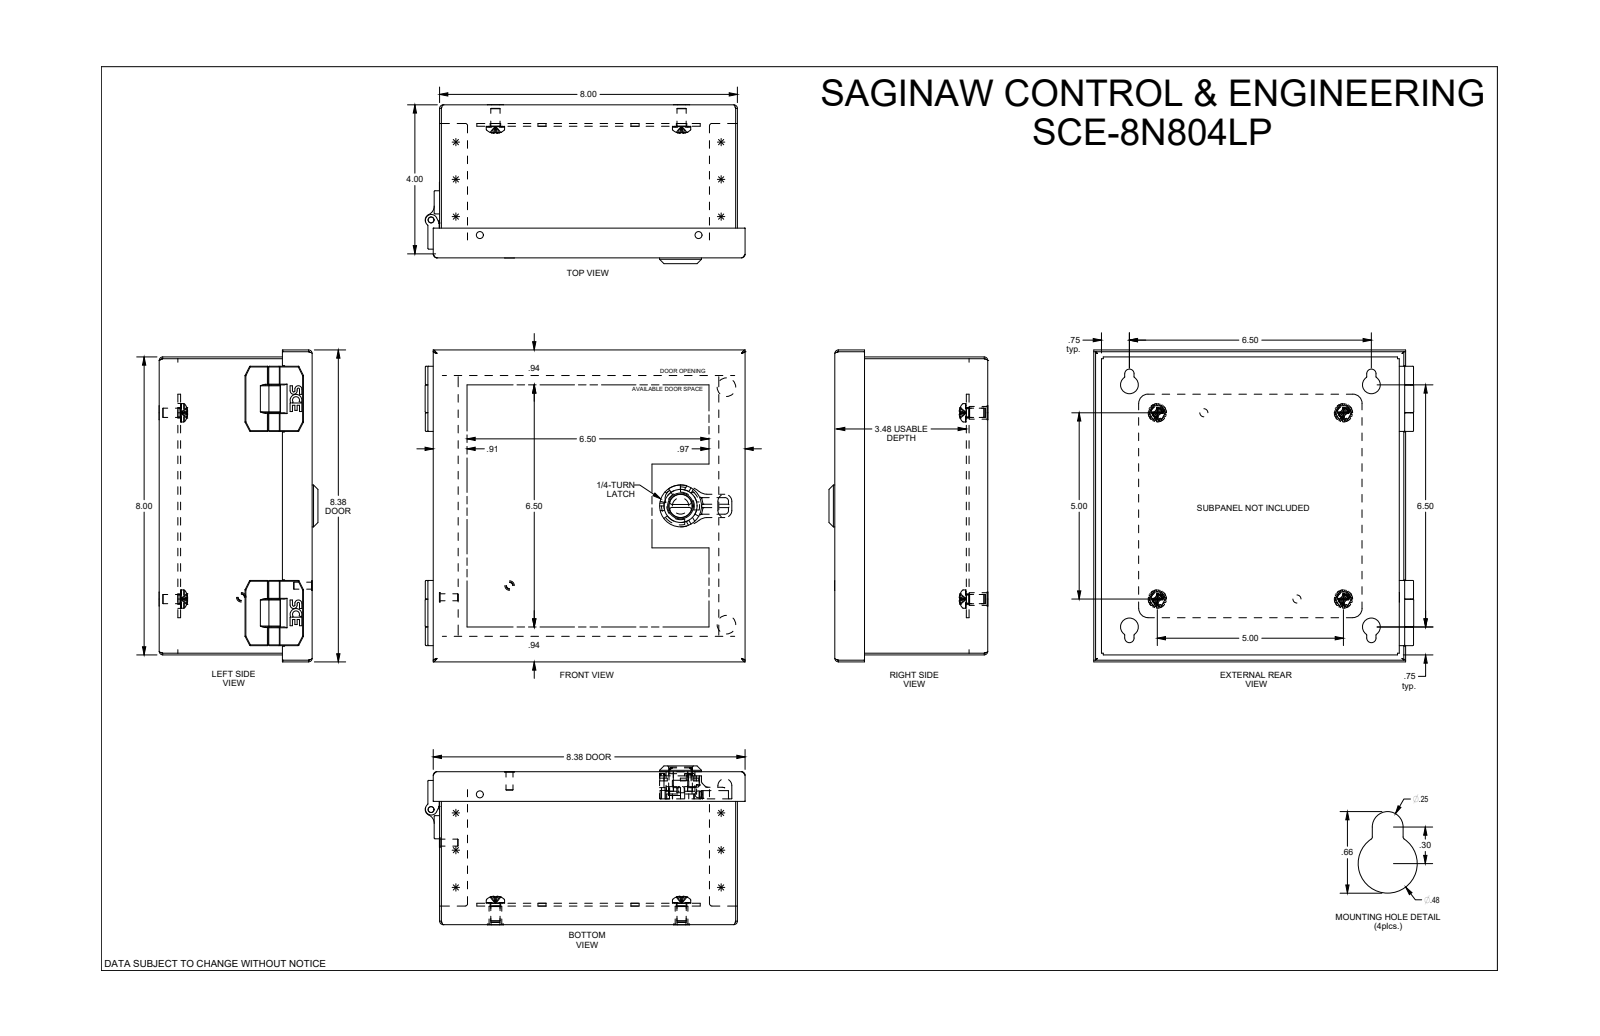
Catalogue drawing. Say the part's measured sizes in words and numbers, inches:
The part is named "SCE-8N804LP_rev1". Its 3-D file was written by "SolidWorks 2021 (AUTOMOTIVE_DESIGN)". It is 23 solids with 746 faces: 249 planar, 318 cylindrical and 179 other. Overall it measures 8.593 by 8.375 by 4.263 inches. Its volume is 22.25 cubic inches and its surface area 707.2 square inches. Round holes: 4 of diameter 0.203, 4 of diameter 0.25, 4 of diameter 0.281, 4 of diameter 0.343, 4 of diameter 0.48, 2 of diameter 0.218, 2 of diameter 0.329, 1 of diameter 0.158, 1 of diameter 0.187, 1 of diameter 0.193, 1 of diameter 0.44, 1 of diameter 0.635. Round bosses or shafts: 4 of diameter 0.376, 4 of diameter 0.237, 4 of diameter 0.16, 2 of diameter 0.5, 2 of diameter 0.323, 2 of diameter 0.248, 1 of diameter 1.125, 1 of diameter 1.125. Partial cylindrical surfaces (rounded edges, fillets, slot ends): 95 of radius 0.02, 25 of radius 0.06, 16 of radius 0.015, 13 of radius 0.01, 6 of radius 0.055, 6 of radius 0.25, 4 of radius 0.125, 3 of radius 0.188. The main face-to-face distances are 0.06, 7.94, 4.047, 7.88, 8, 3.987, 4.107, 0.548, 0.488, 3.499. The hole center spacings are 5.799, 1.061, 5, 6.5, 8.132, 1.25, 2.136, 2.5.
